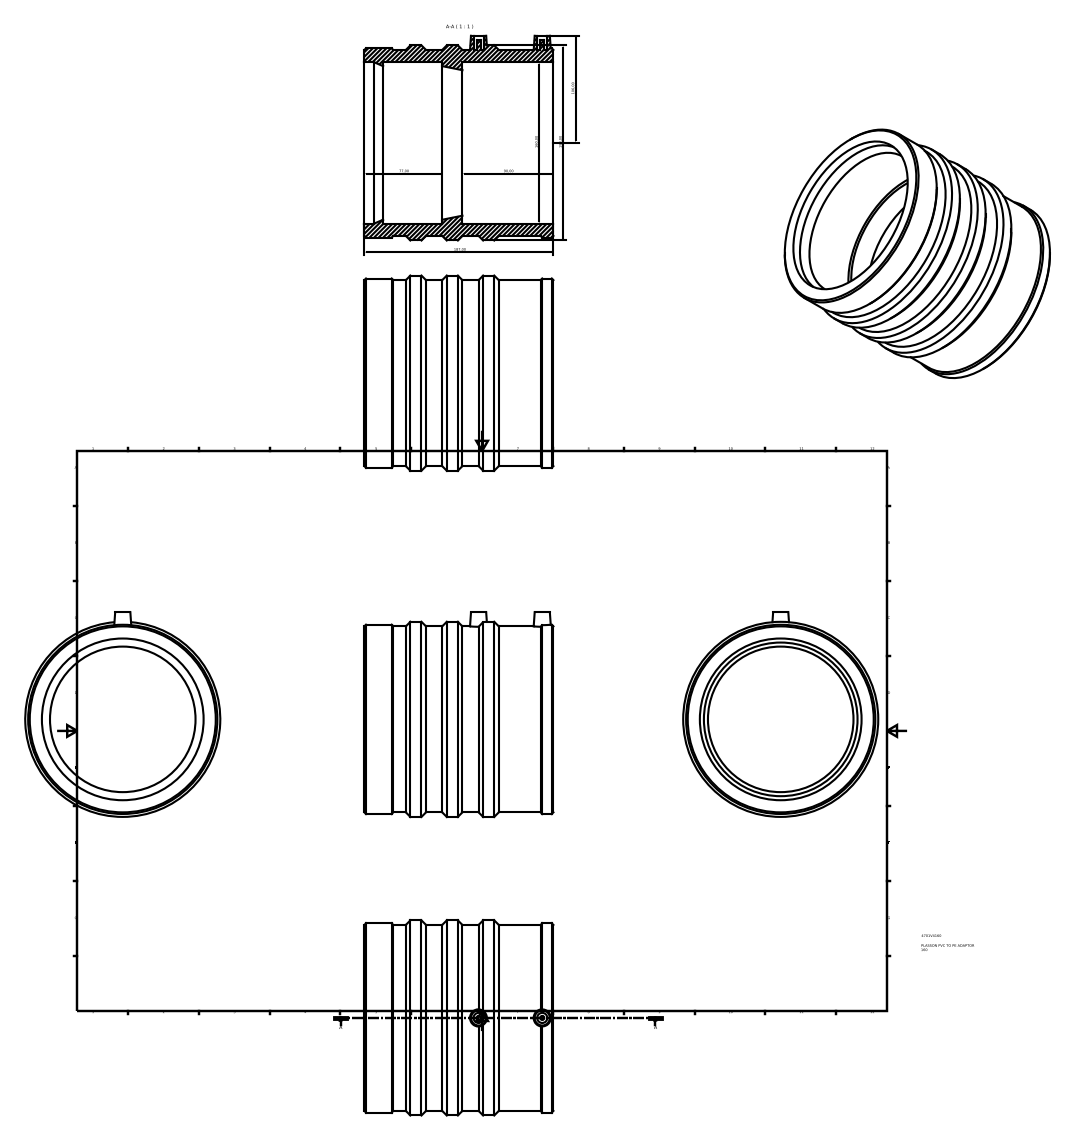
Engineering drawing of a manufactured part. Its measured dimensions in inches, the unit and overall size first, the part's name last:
Units: inches
Overall size (bounding box): 7.972 × 7.598 × 7.362
Round holes (diameter × count): ⌀0.394 ×2, ⌀6.299 ×1
Round bosses / shafts (diameter × count): ⌀0.157 ×2, ⌀7.598 ×1, ⌀7.37 ×1, ⌀7.244 ×1
Main face-to-face distances: 7.362, 3.819, 3.543, 0.728, 3.031, 2.304, 3.091, 6.635, 0.787, 4.331
Hole centre spacings: 2.481
Volume: 88 in³ · Surface area: 363.8 in²
Bodies: 1 solid, 41 faces (11 planar, 16 cylindrical, 14 other)
Part name (STEP PRODUCT): 4701V4160
STEP written by: Autodesk Inventor 2015 (AUTOMOTIVE_DESIGN)
